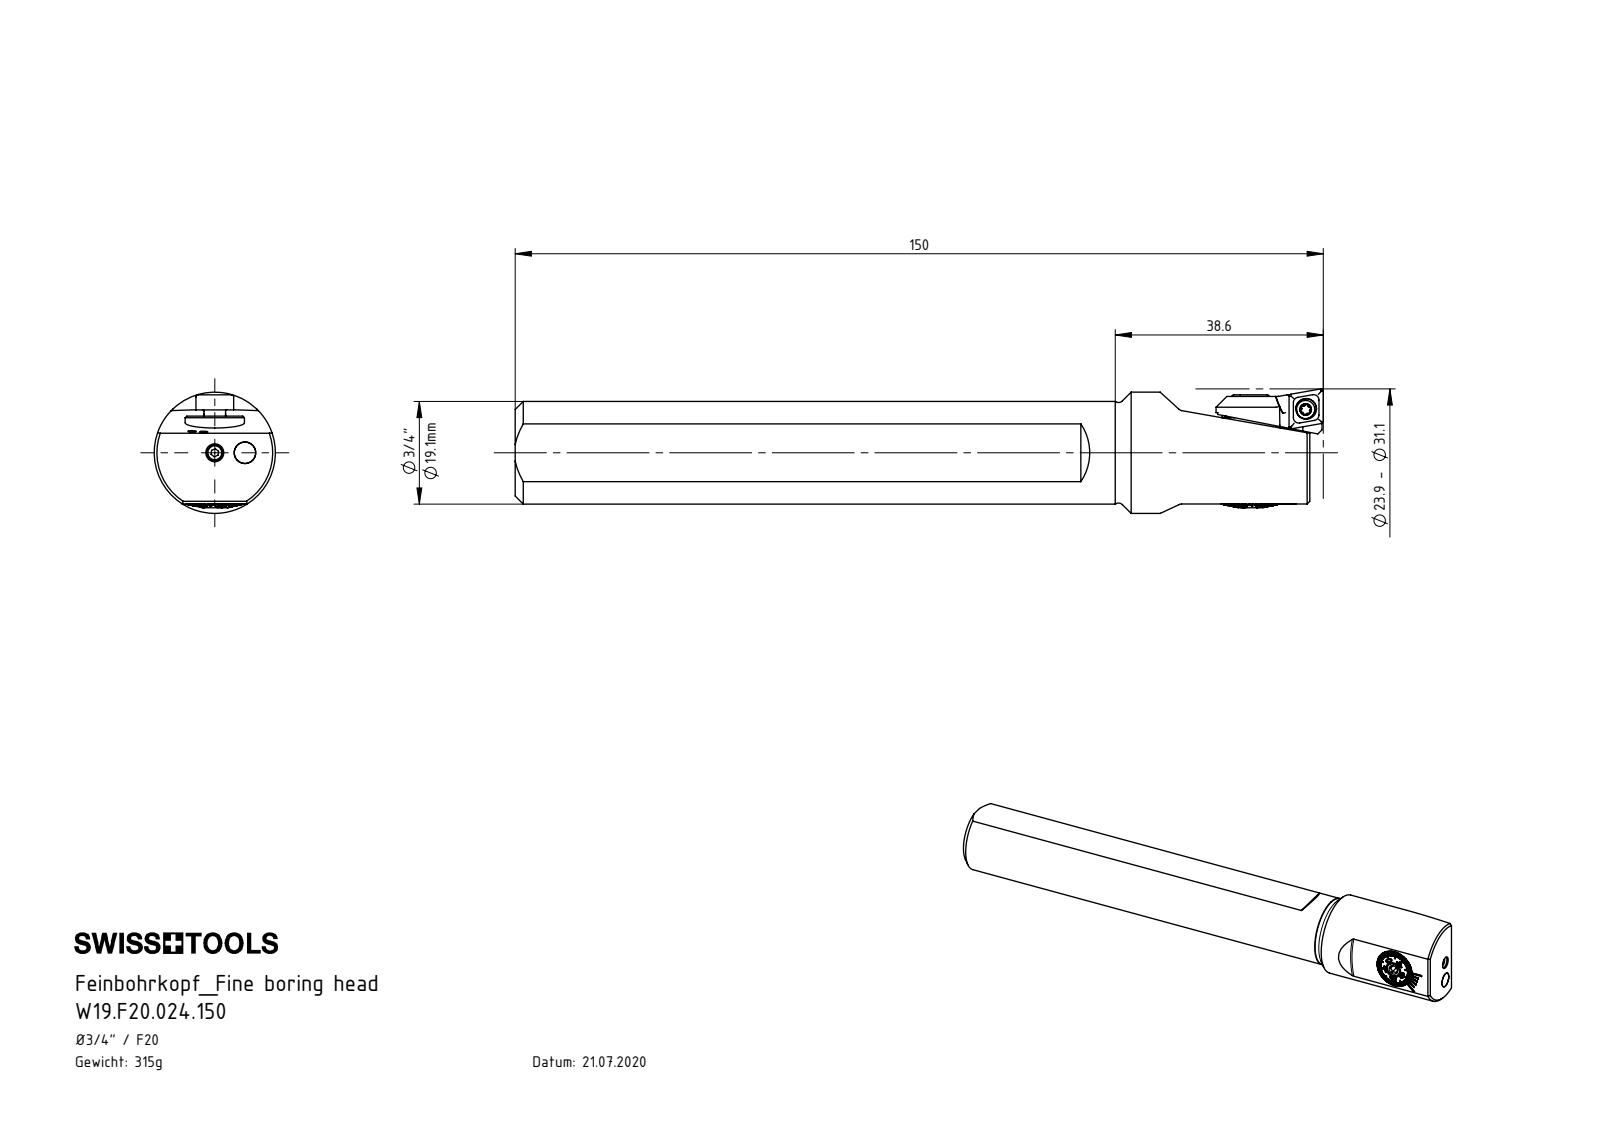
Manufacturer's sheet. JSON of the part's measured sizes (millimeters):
{"part_name": "DIN 7984 - M4 x 6_PreviewCfg; F20-BG2.008.009_A; F20-BG1.AA3.011_A_Standart; W19.F20.AA4.150 (+8 more)", "step_written_by": "SolidWorks 2017 (AUTOMOTIVE_DESIGN)", "units": "millimeters", "bodies": {"solids": 13, "faces": 498, "planar": 286, "cylindrical": 53, "other": 159}, "overall_size": [147.5, 22.5, 22.5], "volume_mm3": 39674, "surface_area_mm2": 15257, "round_holes": [[2.1, 4], [1.5, 2], [3, 2], [3.3, 2], [1.08, 1], [1.9, 1], [4, 1], [4.5, 1], [5, 1], [5.4, 1], [6.2, 1], [6.5, 1]], "round_bosses_or_shafts": [[4, 2], [3.95, 2], [22.5, 1], [19.05, 1], [11, 1], [10.98, 1], [10.85, 1], [8.65, 1]], "partial_cylinders_radius": [[0.3, 2], [1.25, 2], [2, 2]], "face_to_face_distances": [147.5, 3.7, 1.5, 0.8, 2.9, 2.8, 1.4, 12.6, 15.5, 16.3], "hole_center_spacings": [5.38, 5.6, 8.71]}
